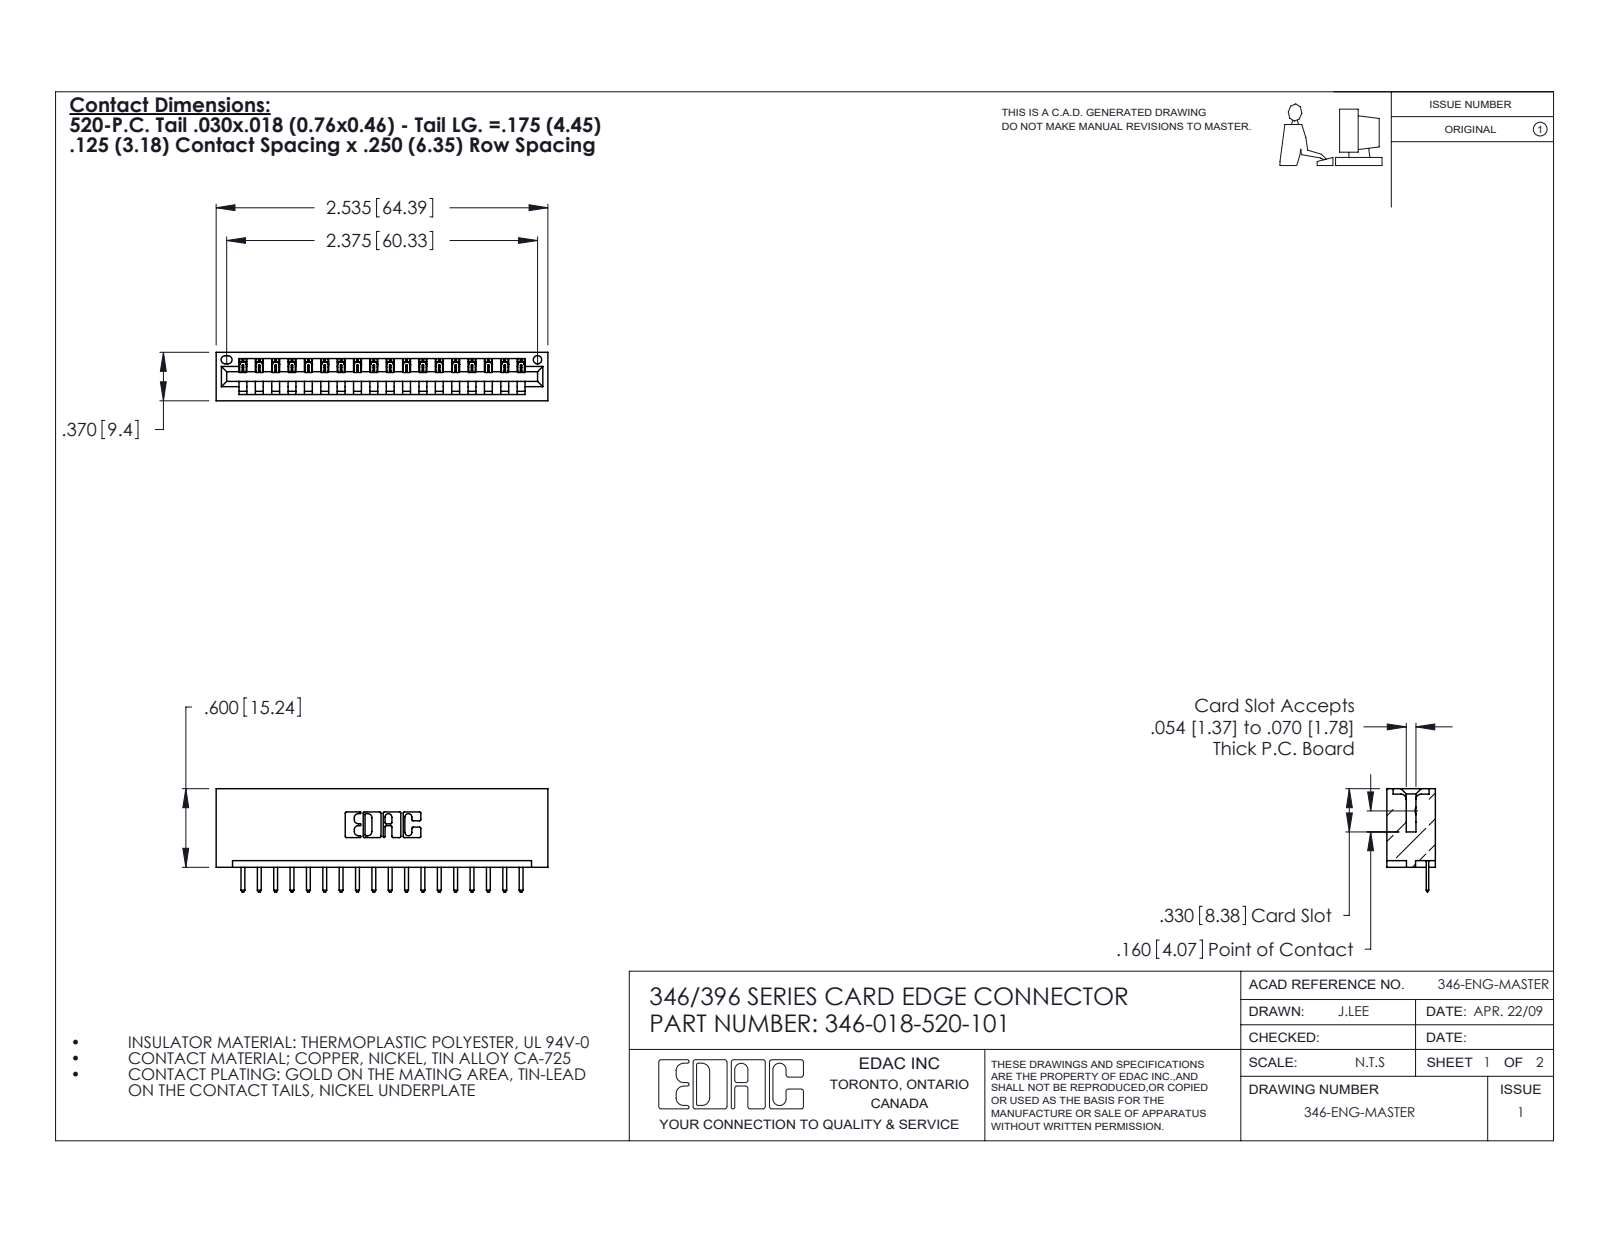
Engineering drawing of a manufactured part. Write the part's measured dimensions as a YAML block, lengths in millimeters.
part_name: "346 Part_No Mounting Lugs; 346-018-520-101; 345-292-001_345-293-120"
step_written_by: "SolidWorks 2020 (CONFIG_CONTROL_DESIGN)"
units: millimeters
bodies: {solids: 19, faces: 1230, planar: 828, cylindrical: 402, other: 0}
overall_size: [64.4, 20, 9.4]
volume: 6490
surface_area: 7761
round_holes:
  - {diameter: 1.6, count: 1}
partial_cylinders:
  - {radius: 0.3, count: 38}
  - {radius: 0.2, count: 36}
  - {radius: 0.3, count: 22}
  - {radius: 0.2, count: 6}
  - {radius: 0.8, count: 6}
  - {radius: 0.7, count: 3}
  - {radius: 0.8, count: 2}
  - {radius: 1, count: 2}
face_to_face_distances: [1.2, 8.2, 9.4, 6.4, 3.8, 5.6, 2.5, 4.4, 1.8, 7.6]
